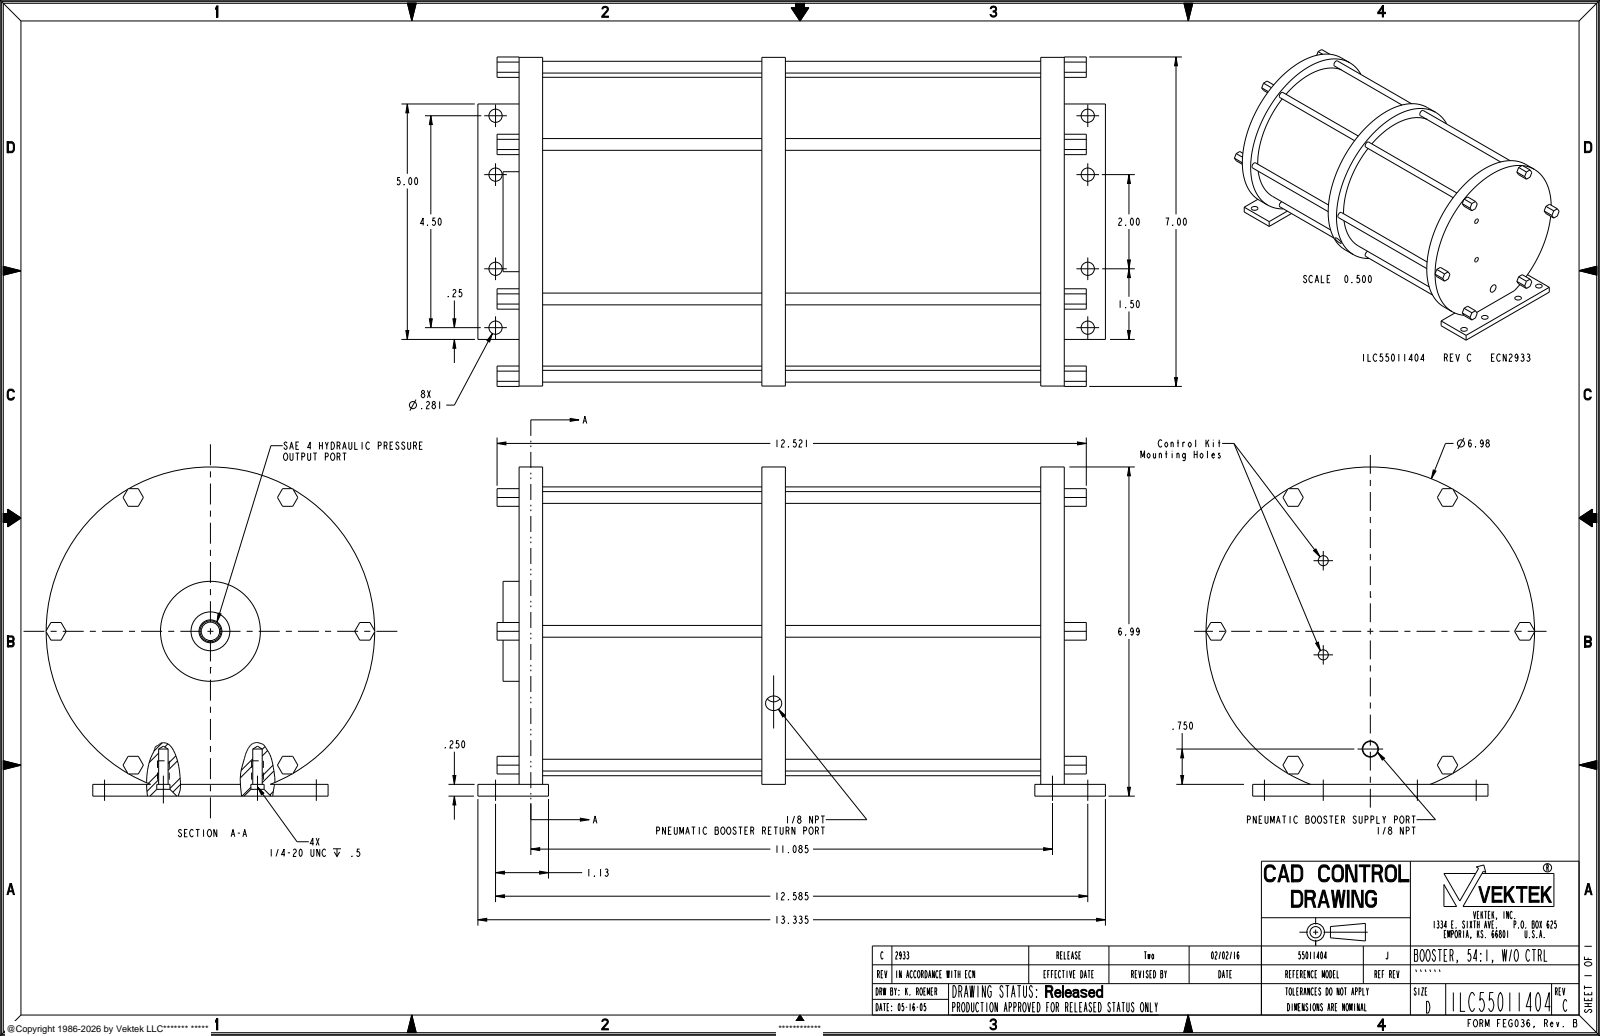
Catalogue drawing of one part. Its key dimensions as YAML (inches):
part_name: "ILC55011404"
step_written_by: "PRO/ENGINEER BY PARAMETRIC TECHNOLOGY CORPORATION, 2013320 (CONFIG_CONTROL_DESIGN)"
units: inches
bodies: {solids: 1, faces: 245, planar: 128, cylindrical: 87, other: 30}
overall_size: [13.335, 6.996, 6.99]
volume: 362.8
surface_area: 431.9
round_holes:
  - {diameter: 0.281, count: 12}
  - {diameter: 0.25, count: 6}
  - {diameter: 0.201, count: 4}
  - {diameter: 0.213, count: 2}
  - {diameter: 0.392, count: 1}
  - {diameter: 0.825, count: 1}
round_bosses_or_shafts:
  - {diameter: 0.25, count: 6}
  - {diameter: 6.98, count: 1}
  - {diameter: 6.133, count: 1}
  - {diameter: 2.123, count: 1}
  - {diameter: 0.437, count: 1}
face_to_face_distances: [11.585, 0.5, 11.085, 5.159, 5.926, 0.25, 5.659, 4.659, 10.585, 6.426]
hole_center_spacings: [2, 0.75, 1.25, 1.458, 2.136, 3.25, 3.335, 11.835]
